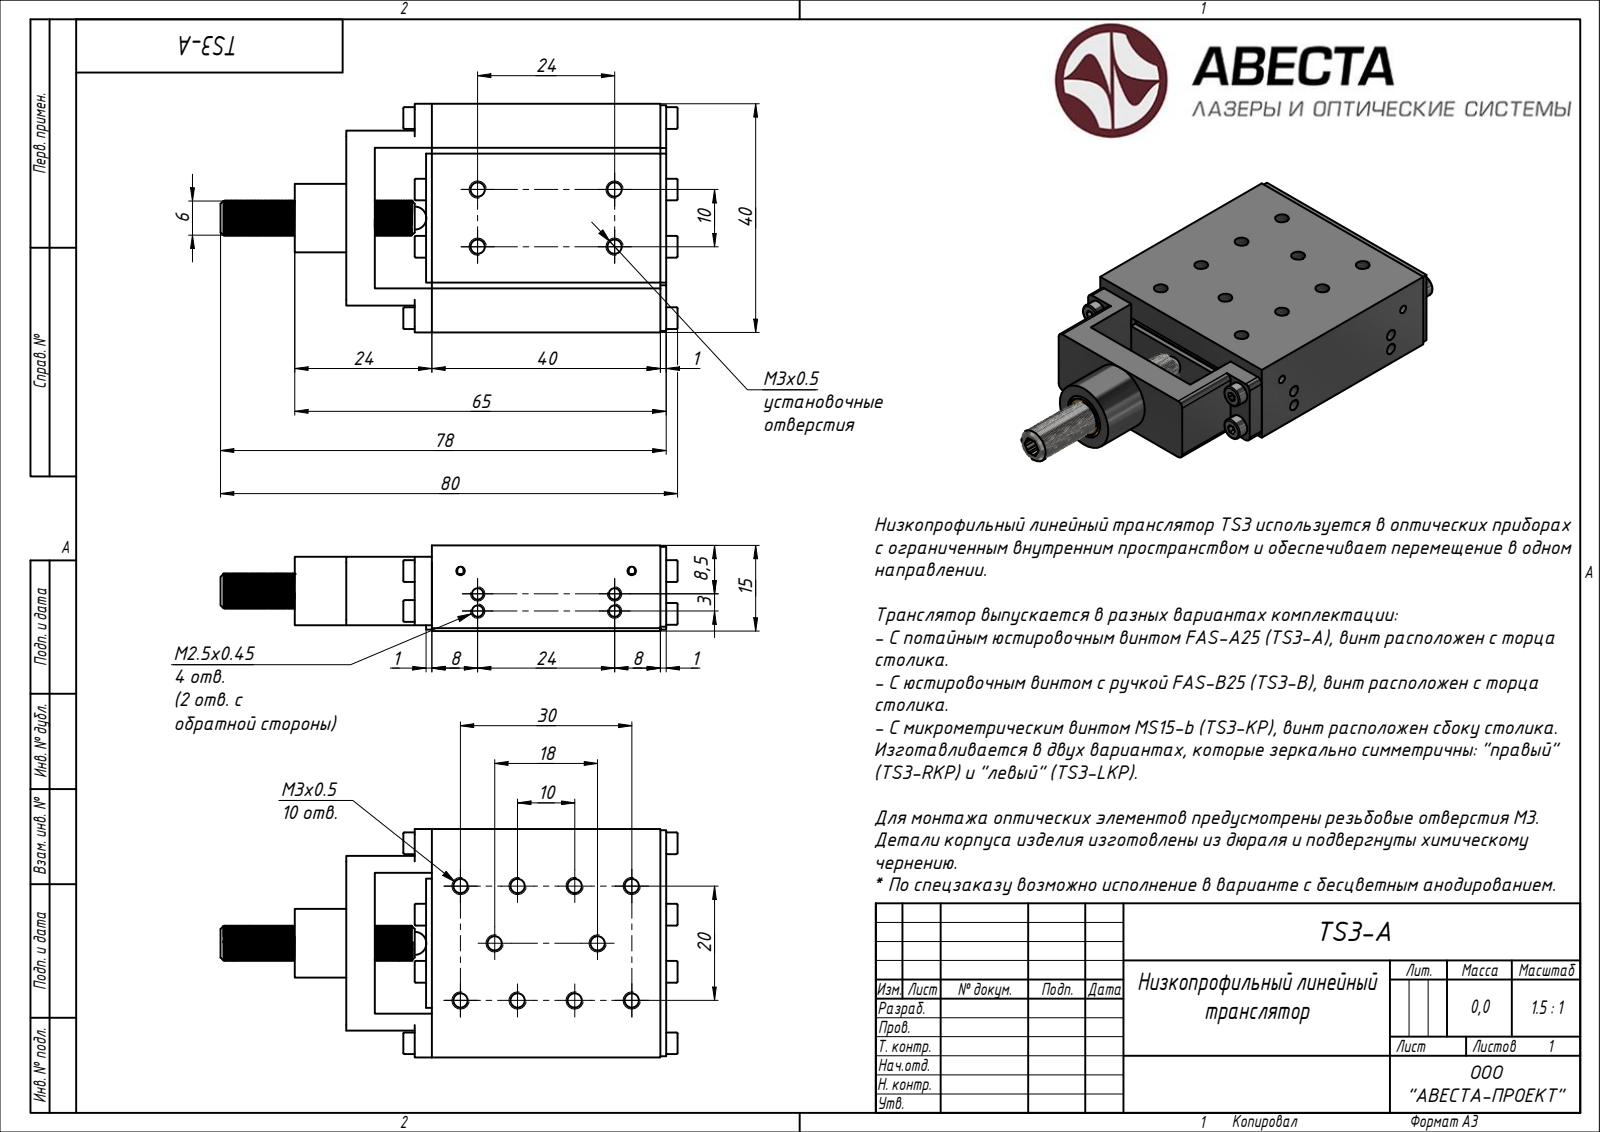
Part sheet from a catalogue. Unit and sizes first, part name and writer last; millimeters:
Units: millimetres
Overall size (bounding box): 80 × 40 × 15
Round holes (diameter × count): ⌀2.46 ×14, ⌀2.5 ×5, ⌀1.5 ×4, ⌀2.85 ×4, ⌀1.57 ×3, ⌀1.57 ×3, ⌀2 ×2, ⌀2.01 ×2, ⌀2.01 ×2, ⌀2.46 ×1, ⌀3.1 ×1, ⌀6 ×1
Round bosses / shafts (diameter × count): ⌀3.8 ×6, ⌀2 ×5, ⌀3 ×4, ⌀12 ×1, ⌀9 ×1, ⌀6 ×1
Partial cylindrical surfaces — rounded edges, fillets, slot ends (radius × count): R1 ×8, R2 ×4, R1.1 ×2, R1.23 ×1, R1.23 ×1
Main face-to-face distances: 0.5, 5, 9.5, 2, 7, 3, 10, 9, 15, 1
Hole centre spacings: 5.83, 10, 20, 26, 24, 1.5, 3, 11.66
Volume: 24 216 mm³ · Surface area: 17 801 mm²
Bodies: 1 solid, 654 faces (234 planar, 306 cylindrical, 114 other)
STEP written by: Rhino 7.34 (AUTOMOTIVE_DESIGN)
